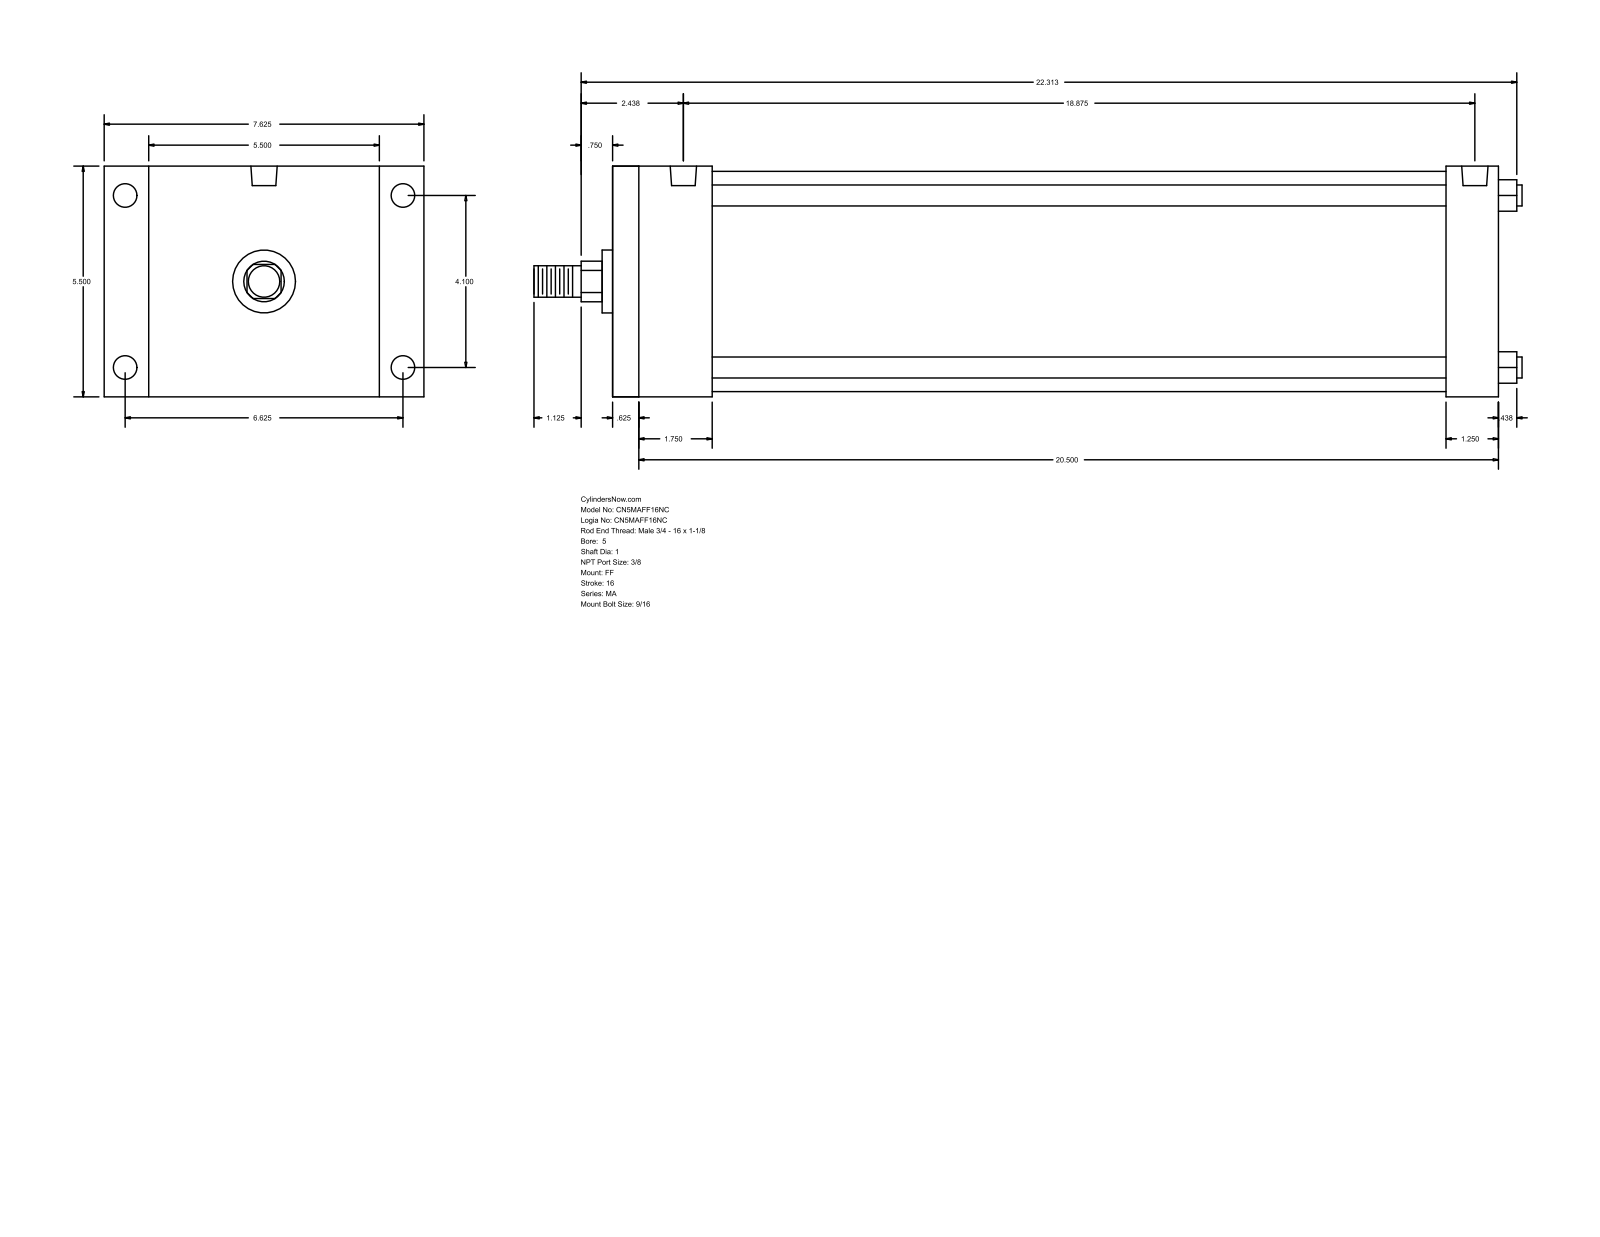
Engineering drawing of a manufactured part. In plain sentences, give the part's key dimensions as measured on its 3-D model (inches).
The part is named "MA_FF__0500_1". Its 3-D file was written by "GSSL Pune (CONFIG_CONTROL_DESIGN)". It is 0 solids with 92 faces: 64 planar, 28 cylindrical and 0 other. Overall it measures 23.563 by 7.625 by 5.5 inches. Round holes: 4 of diameter 0.437, 4 of diameter 0.563, 2 of diameter 0.627. Round bosses or shafts: 4 of diameter 0.5, 1 of diameter 5.25, 1 of diameter 1.5, 1 of diameter 1, 1 of diameter 0.75. Partial cylindrical surfaces (rounded edges, fillets, slot ends): 1 of radius 0.484. The main face-to-face distances are 5.5, 21.125, 0.625, 20.5, 19.875, 19.25, 1.25, 2.375, 1.75, 17.5. The hole center spacings are 0.187, 4.1, 6.625, 7.791, 18.5, 18.688, 18.875.
